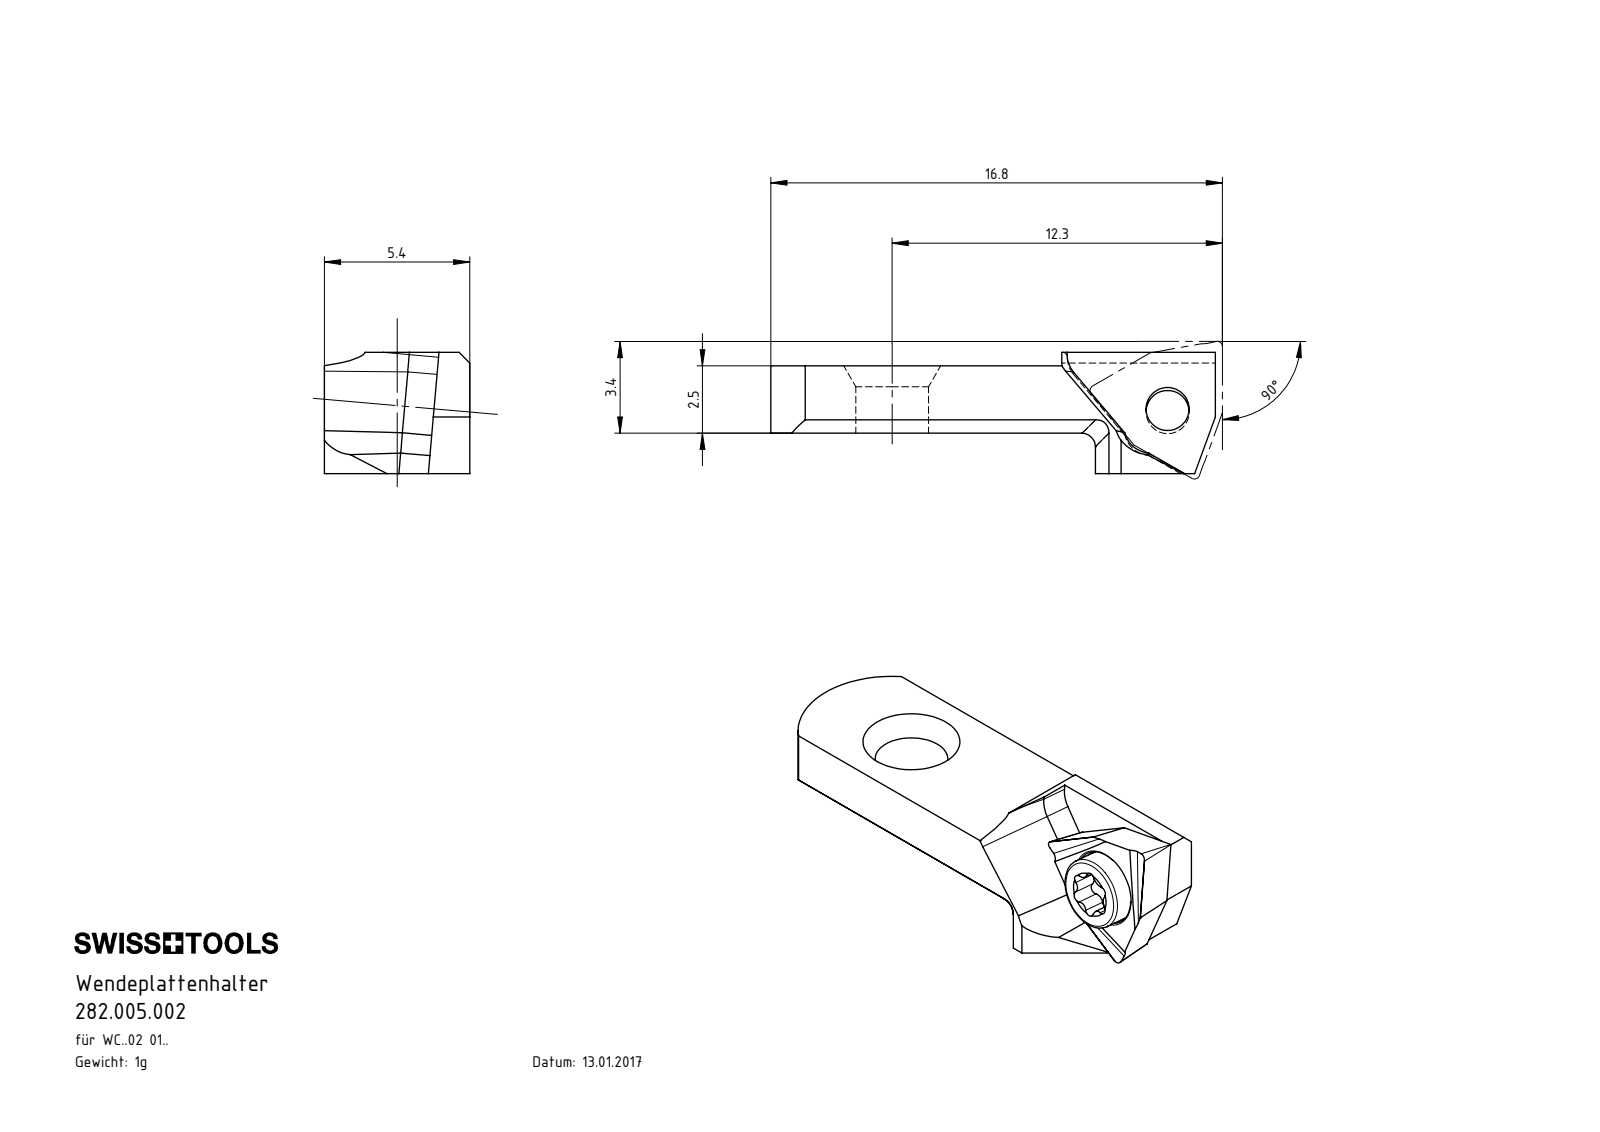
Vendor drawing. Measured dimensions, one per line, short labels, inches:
name: 282.005.002; WWA-ER2.001.004_A; F14-WWA.001.004_C; WWA-SFH.020.004
written by: SolidWorks 2017 (CONFIG_CONTROL_DESIGN)
unit: in
bodies: 3 solids, 100 faces (40 planar, 34 cylindrical, 26 other)
size: 0.66 × 0.22 × 0.201
volume: 0.012 in³; area: 0.6 in²
holes: 1× ⌀0.063, 1× ⌀0.091, 1× ⌀0.106
bosses: 1× ⌀0.106, 1× ⌀0.079
rounds: 6× R0.007, 6× R0.013, 3× R0.012, 2× R0.028, 2× R0.039, 1× R0.02, 1× R0.138
face distances: 0.098, 0.213, 0.059, 0.157, 0.177, 0.118, 0.02, 0.063, 0.209, 0.088
